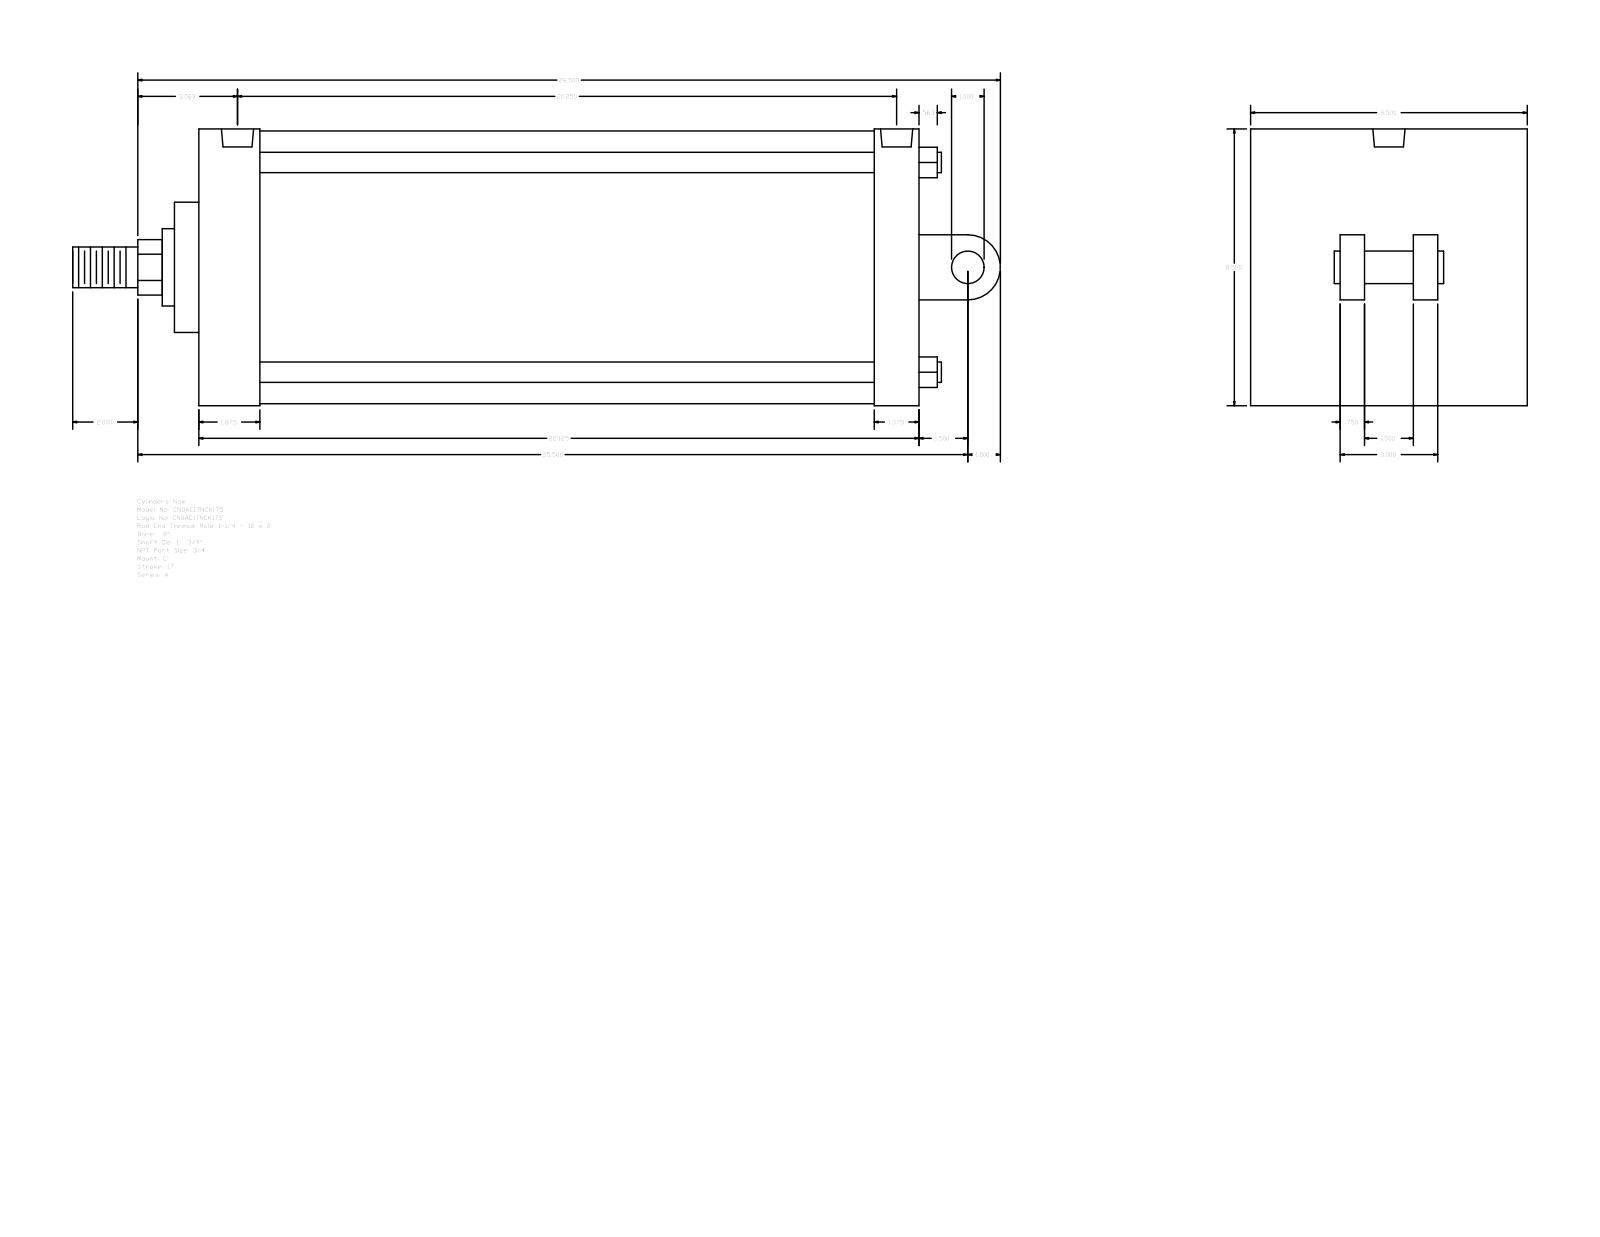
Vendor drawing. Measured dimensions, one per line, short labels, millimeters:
name: A_C__0800_1.75
written by: GSSL Pune (CONFIG_CONTROL_DESIGN)
unit: mm
bodies: 0 solids, 104 faces (75 planar, 29 cylindrical, 0 other)
size: 723.9 × 215.9 × 215.9
holes: 4× ⌀15.08, 2× ⌀25.12
bosses: 4× ⌀15.88, 1× ⌀212.72, 1× ⌀60.33, 1× ⌀44.45, 1× ⌀31.75, 1× ⌀25.4
rounds: 1× R21.63, 1× R25.4
face distances: 561.98, 215.9, 19.05, 57.15, 47.63, 514.35, 527.05, 479.42, 34.93, 69.85
hole spacings: 6.35, 501.65, 508, 514.35
